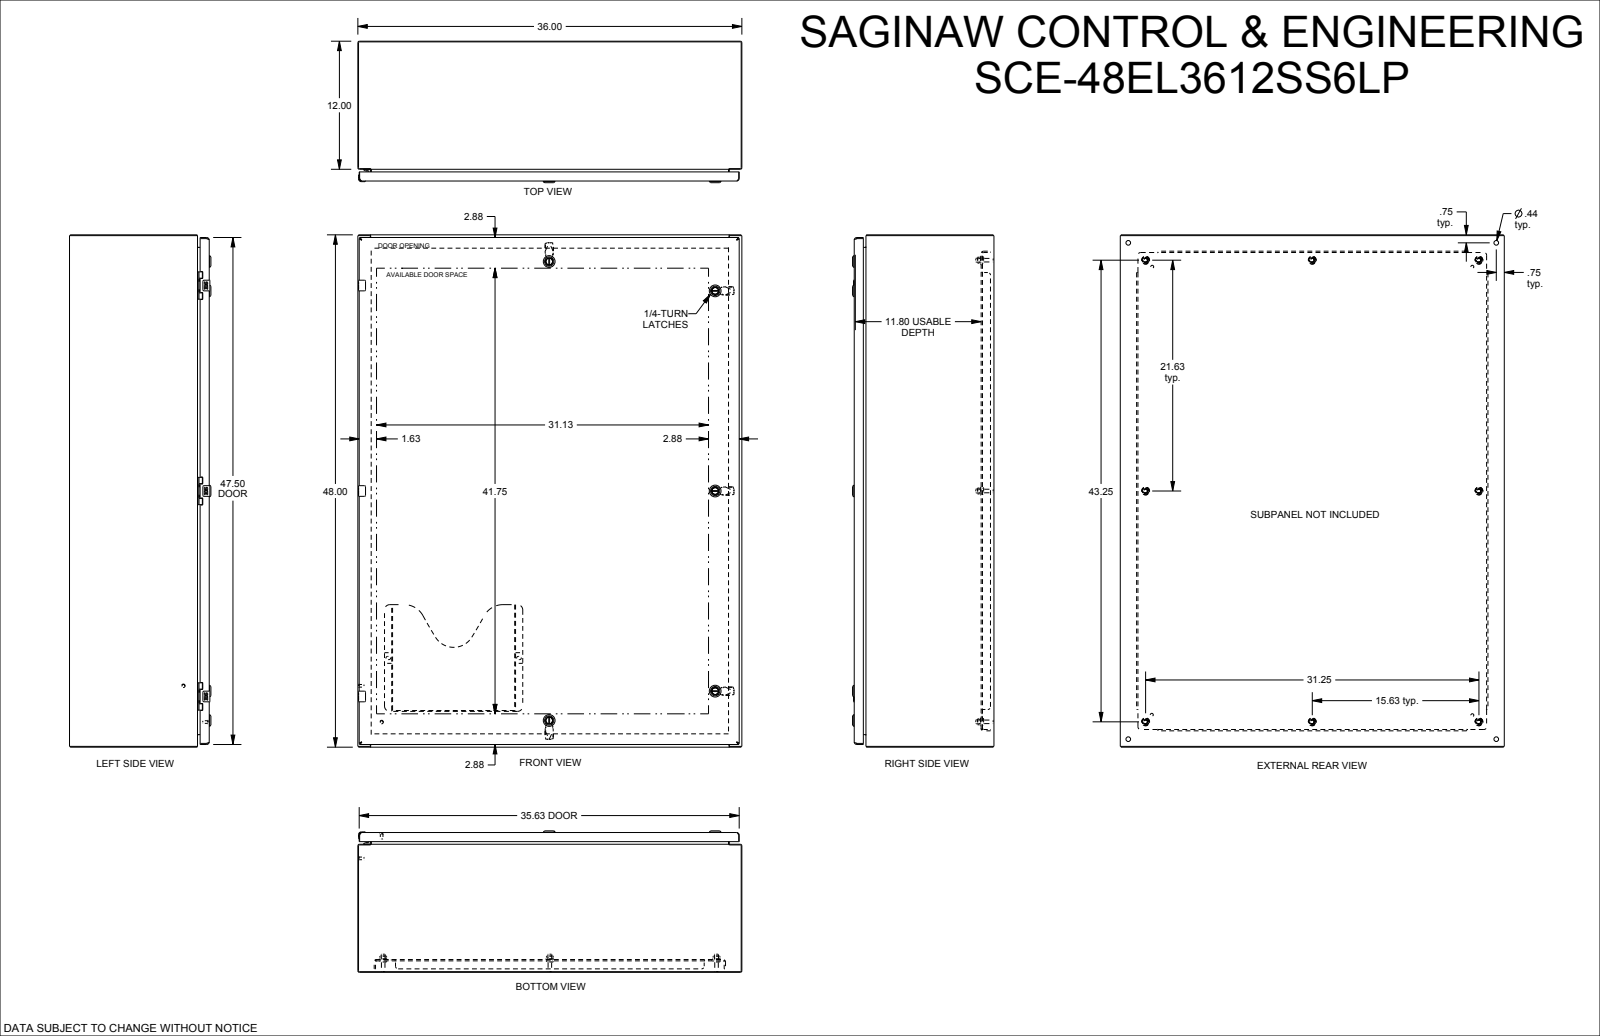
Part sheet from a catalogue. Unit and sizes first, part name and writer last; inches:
Units: inches
Overall size (bounding box): 48 × 36 × 13.256
Round holes (diameter × count): ⌀0.367 ×8, ⌀0.5 ×8, ⌀0.172 ×6, ⌀0.205 ×6, ⌀0.244 ×6, ⌀0.266 ×6, ⌀0.197 ×5, ⌀0.315 ×5, ⌀0.394 ×5, ⌀0.634 ×5, ⌀0.281 ×4, ⌀0.375 ×4
Round bosses / shafts (diameter × count): ⌀0.17 ×9, ⌀0.366 ×8, ⌀0.332 ×8, ⌀0.25 ×6, ⌀1.102 ×5, ⌀0.866 ×5, ⌀0.802 ×5, ⌀0.78 ×5
Partial cylindrical surfaces — rounded edges, fillets, slot ends (radius × count): R0.012 ×142, R0.01 ×52, R0.02 ×52, R0.015 ×36, R0.04 ×23, R0.157 ×20, R0.07 ×14, R0.03 ×13
Main face-to-face distances: 0.075, 0.104, 12.92, 12.995, 13.099, 13.024, 1.125, 11.795, 1, 11.92
Hole centre spacings: 19.25, 38.5, 0.049, 0.986, 18.265, 19.25, 19.25, 20.235
Bodies: 0 solids, 4752 faces (2321 planar, 1312 cylindrical, 1119 other)
Part name (STEP PRODUCT): SCE-48EL3612SS6LP
STEP written by: SolidWorks 2019 (CONFIG_CONTROL_DESIGN)
